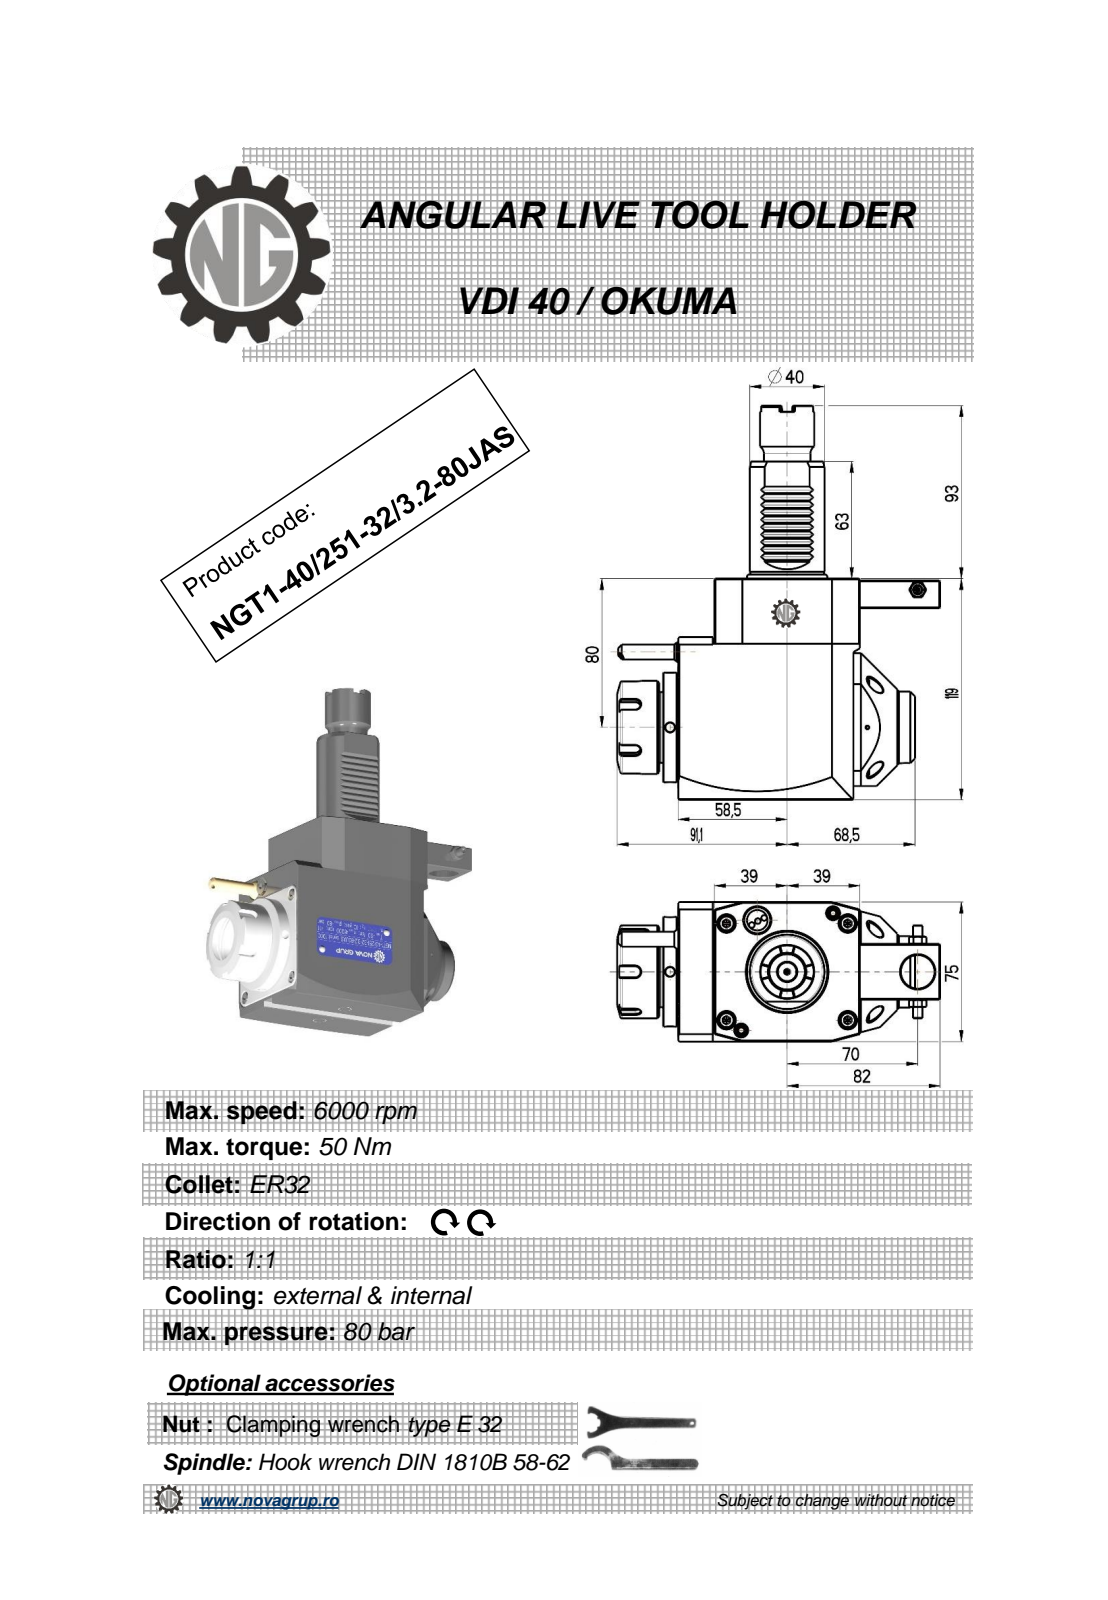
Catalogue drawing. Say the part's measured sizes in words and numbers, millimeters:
The part is named "NGT1_40_251_32_3_2_80JAS". Its 3-D file was written by "PRO/ENGINEER BY PARAMETRIC TECHNOLOGY CORPORATION, 2010280 (CONFIG_CONTROL_DESIGN)". It is 1 solid with 499 faces: 226 planar, 99 cylindrical and 174 other. Overall it measures 212 by 173.1 by 75 millimeters. Its volume is 1 044 000 cubic millimeters and its surface area 84 528 square millimeters. Round holes: 3 of diameter 5, 1 of diameter 3, 1 of diameter 4.2, 1 of diameter 9.5, 1 of diameter 18, 1 of diameter 27, 1 of diameter 46. Round bosses or shafts: 1 of diameter 59, 1 of diameter 50, 1 of diameter 46, 1 of diameter 41, 1 of diameter 40, 1 of diameter 38.5, 1 of diameter 29, 1 of diameter 25. Partial cylindrical surfaces (rounded edges, fillets, slot ends): 12 of radius 0.26, 10 of radius 0.3, 6 of radius 0.2, 5 of radius 3, 2 of radius 5.8, 2 of radius 6, 2 of radius 600, 1 of radius 0.5. The main face-to-face distances are 75, 119, 19.5, 97.5, 78, 19.3, 97.3, 27.5, 3.5, 105.5. The hole center spacings are 36.47, 44.12, 72.5, 132.75, 151.98.
